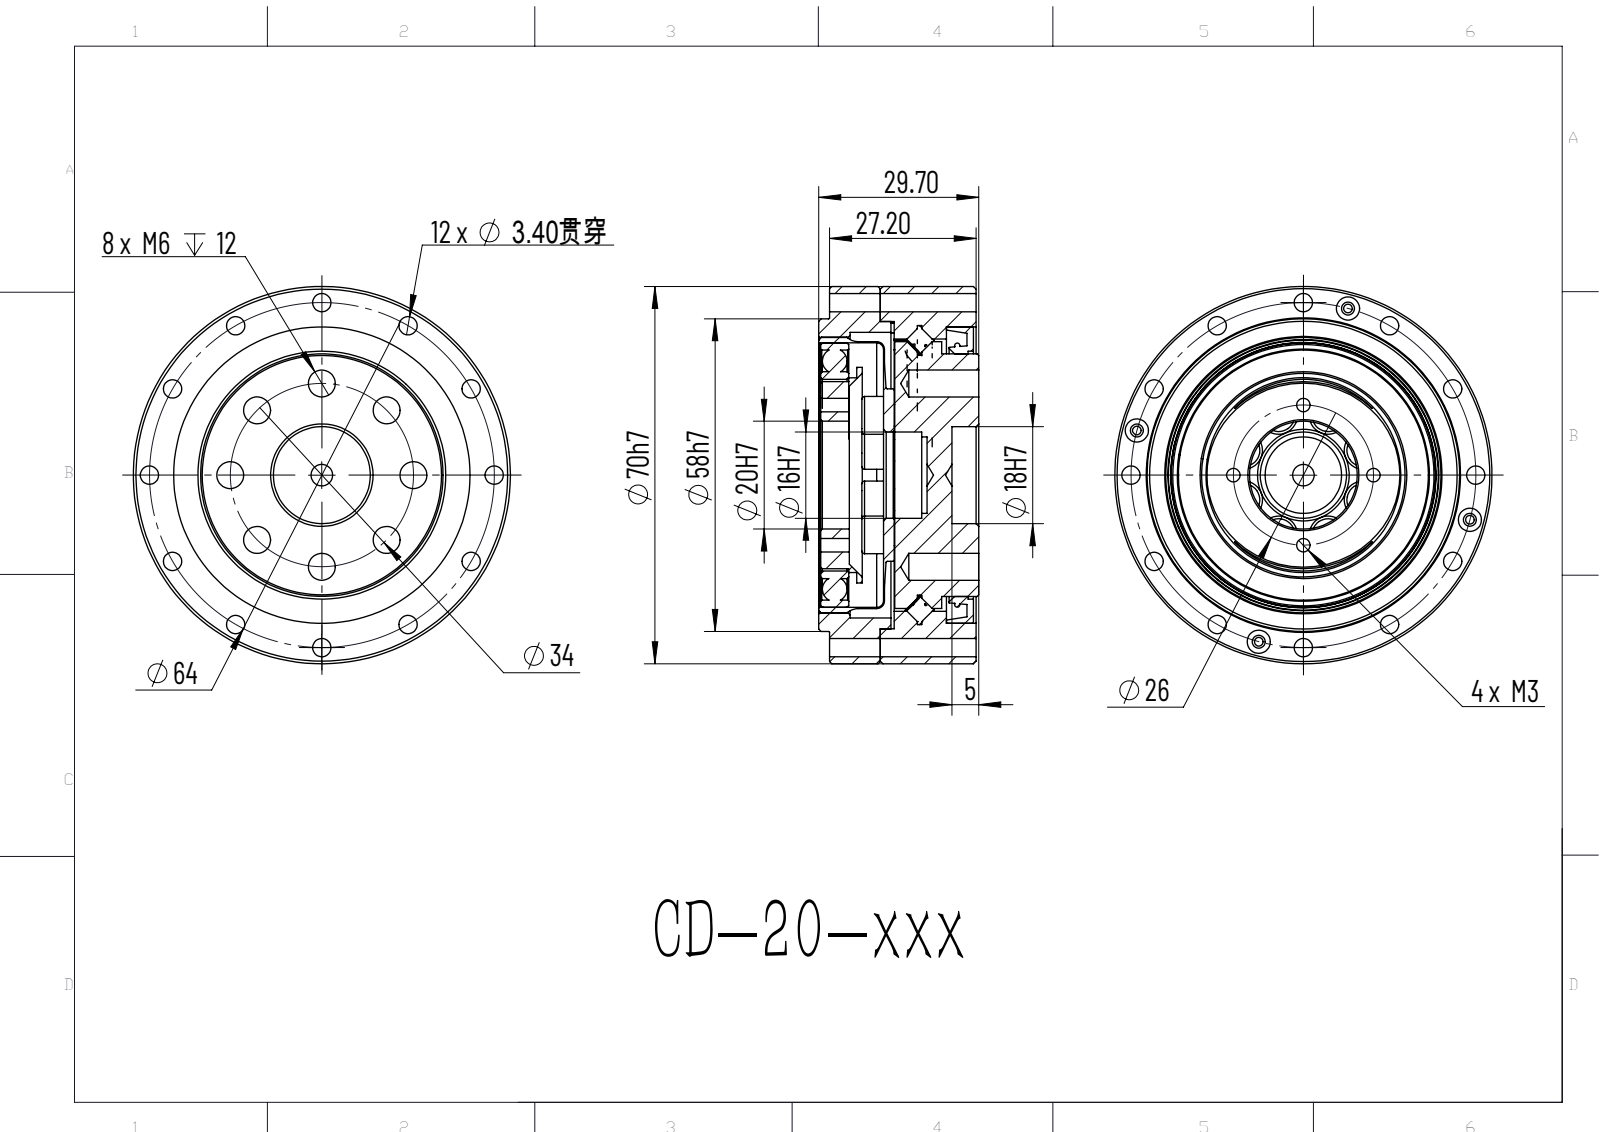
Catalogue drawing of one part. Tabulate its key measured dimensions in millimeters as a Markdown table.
| quantity | value |
| --- | --- |
| part name | CD-20; 20-??; hexagon socket head cap screws gb_GB_FASTENER_SCREWS_HSHCS M4X8-N; CD-20???? <1> (+4 more) |
| STEP written by | ONSHAPE BY PTC INC, 1.201 (AP242_MANAGED_MODEL_BASED_3D_ENGINEERING_MIM_LF) |
| units | millimeters |
| bodies | 20 solids, 457 faces (210 planar, 129 cylindrical, 118 other) |
| overall size | 70 × 70 × 29.7 |
| volume | 79 270 mm³ |
| surface area | 54 353 mm² |
| round holes (diameter × count) | 3.4 × 12, 5 × 9, 3.3 × 8, 4.5 × 8, 1.6 × 4, 2.4 × 4, 2.5 × 4, 4.3 × 4, 2.05 × 1, 2.9 × 1, 14.2 × 1, 16 × 1 |
| round bosses / shafts (diameter × count) | 7 × 8, 4 × 8, 3.8 × 4, 2 × 4, 70 × 1, 58 × 1, 51.21 × 1, 49.55 × 1 |
| main face-to-face distances | 0.6, 2, 0.5, 2.7, 2.1, 17.2, 12, 15.1, 17.8, 5.7 |
| hole center spacings | 32, 45.25, 20.16, 35.61, 40.44, 42.16, 55.42, 61.82 |
